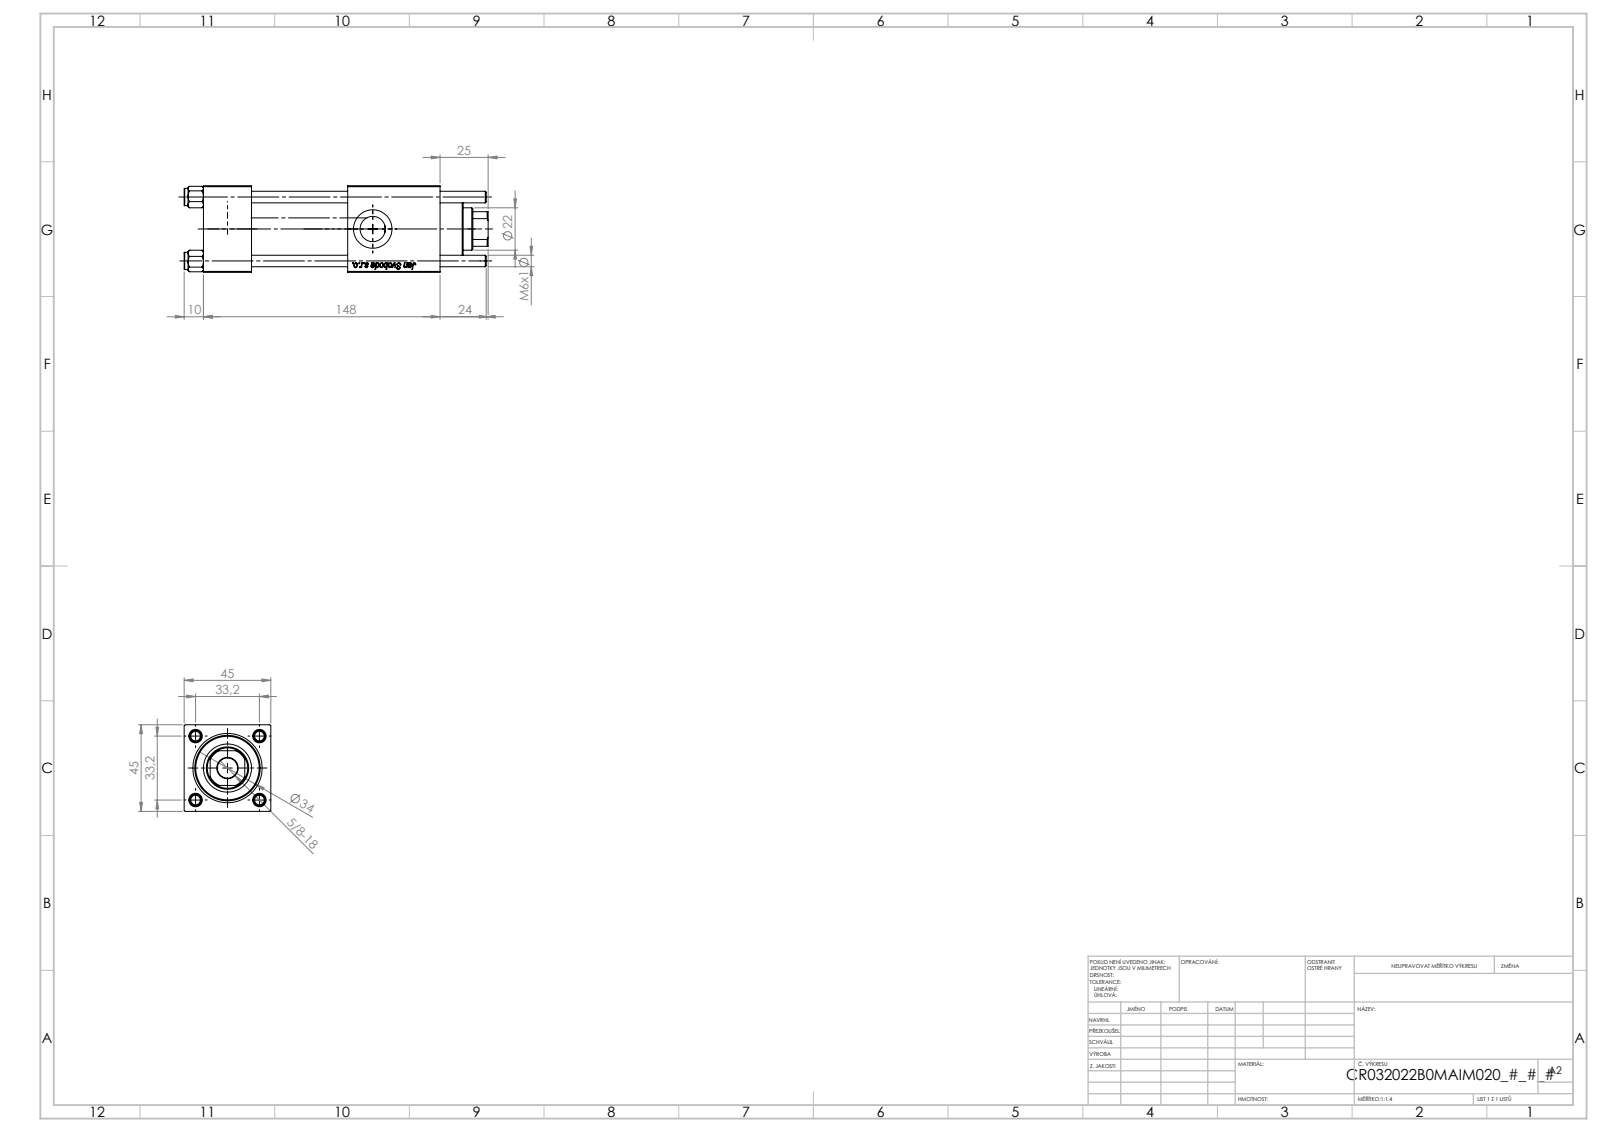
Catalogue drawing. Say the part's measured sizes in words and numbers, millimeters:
The part is named "V215CR_VCP_B; V215_VC_A; V215CR_B-1; NUT_M5_B (+1 more)". Its 3-D file was written by "SolidWorks 2019 (CONFIG_CONTROL_DESIGN)". It is 11 solids with 1156 faces: 429 planar, 79 cylindrical and 648 other. Overall it measures 158 by 45 by 45 millimeters. Its volume is 214 286 cubic millimeters and its surface area 76 783 square millimeters. Round holes: 4 of diameter 6, 2 of diameter 7, 2 of diameter 13.16, 1 of diameter 10.5, 1 of diameter 13, 1 of diameter 20, 1 of diameter 22, 1 of diameter 24, 1 of diameter 25, 1 of diameter 32, 1 of diameter 33. Round bosses or shafts: 4 of diameter 9, 1 of diameter 38, 1 of diameter 34. Partial cylindrical surfaces (rounded edges, fillets, slot ends): 1 of radius 10.5. The main face-to-face distances are 45, 25, 50, 123, 75, 98, 48, 94.3, 69.3, 19.3. The hole center spacings are 23.48, 33.2, 46.95.
